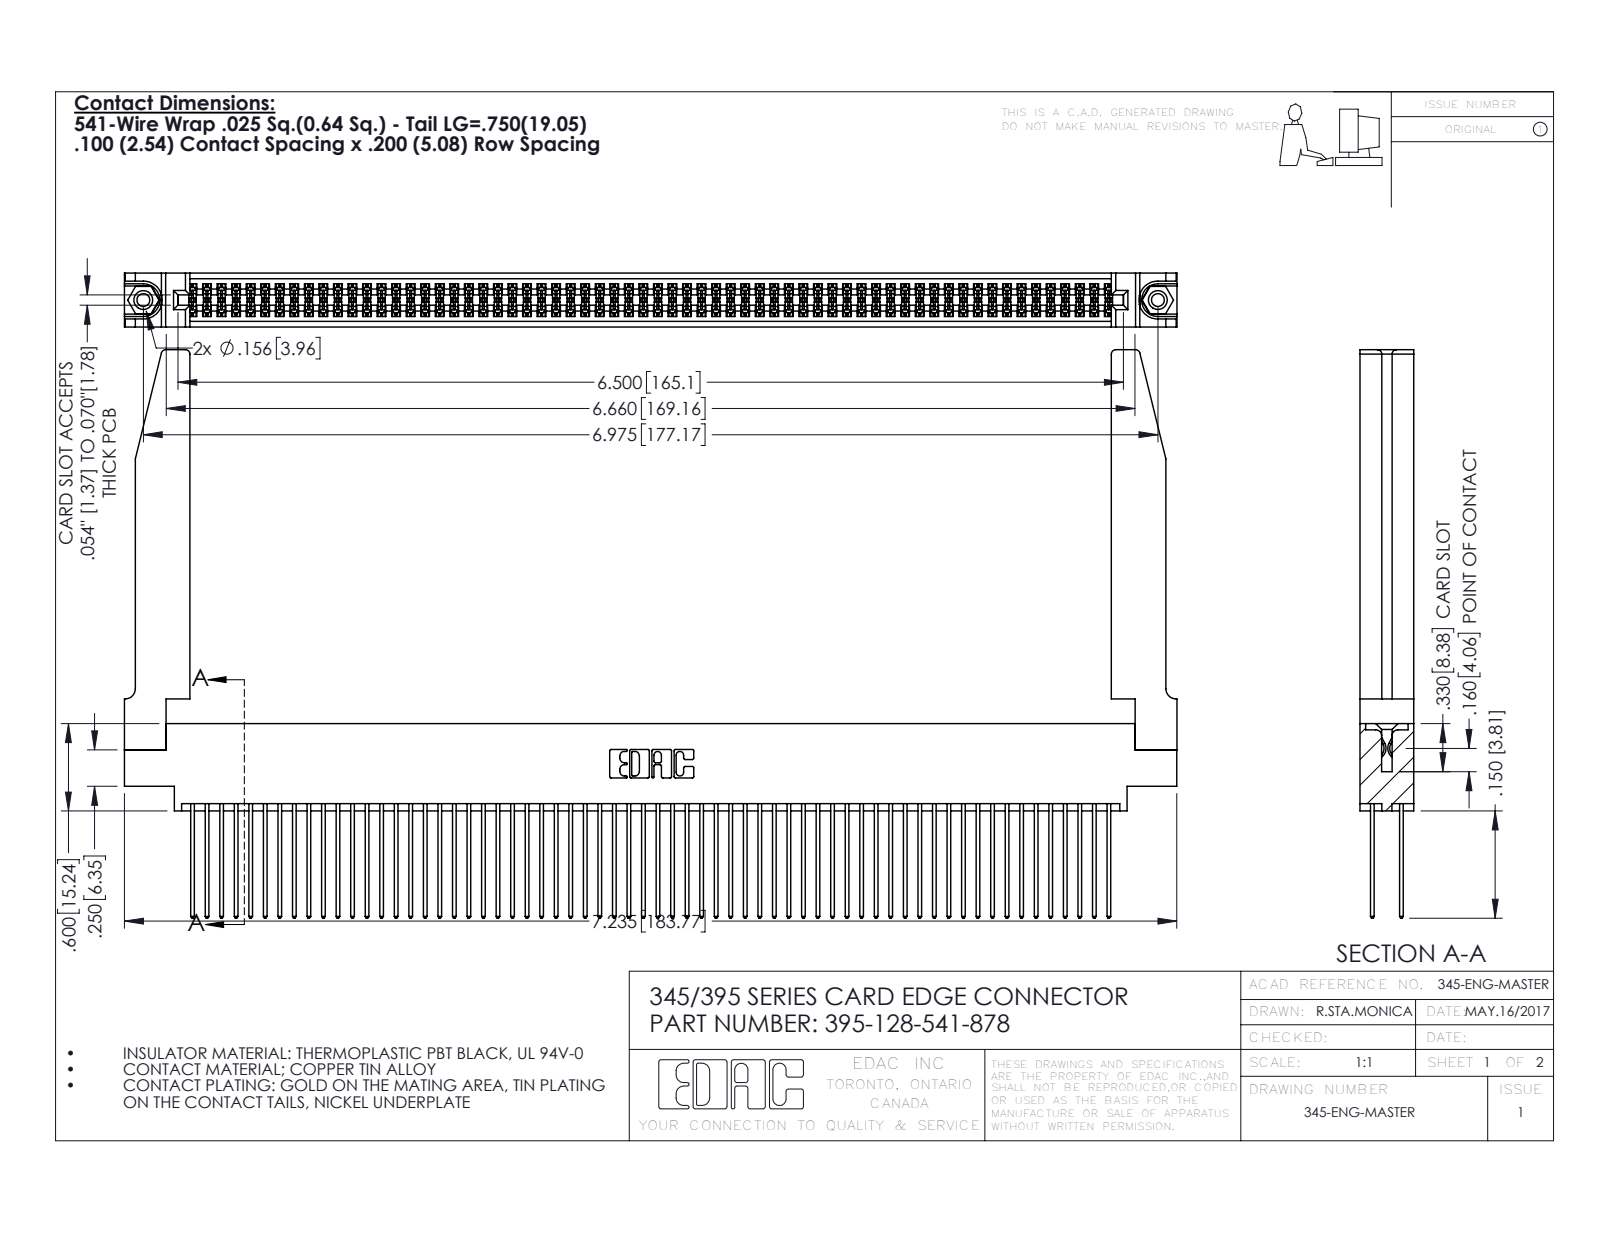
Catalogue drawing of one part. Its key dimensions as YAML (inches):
part_name: "345-220-078_345-220-078; 345-292-001_345-293-141; 345 Part_0.170 Offset - 0.156 Dia-TH; 345-250-001_345-250-001-102 (+1 more)"
step_written_by: "SolidWorks 2016 (CONFIG_CONTROL_DESIGN)"
units: inches
bodies: {solids: 133, faces: 6764, planar: 4450, cylindrical: 2262, other: 52}
overall_size: [7.236, 3.907, 0.37]
volume: 1.614
surface_area: 59.63
round_holes:
  - {diameter: 0.089, count: 2}
  - {diameter: 0.125, count: 2}
  - {diameter: 0.156, count: 2}
  - {diameter: 0.064, count: 1}
round_bosses_or_shafts:
  - {diameter: 0.155, count: 2}
partial_cylinders:
  - {radius: 0.006, count: 192}
  - {radius: 0.01, count: 128}
  - {radius: 0.01, count: 22}
  - {radius: 0.03, count: 8}
  - {radius: 0.007, count: 6}
  - {radius: 0.031, count: 6}
  - {radius: 0.026, count: 3}
  - {radius: 0.014, count: 2}
face_to_face_distances: [0.072, 0.298, 0.37, 0.098, 0.272, 0.025, 0.2, 0.225, 0.175, 0.148]
hole_center_spacings: [0.27, 6.739, 6.975]
